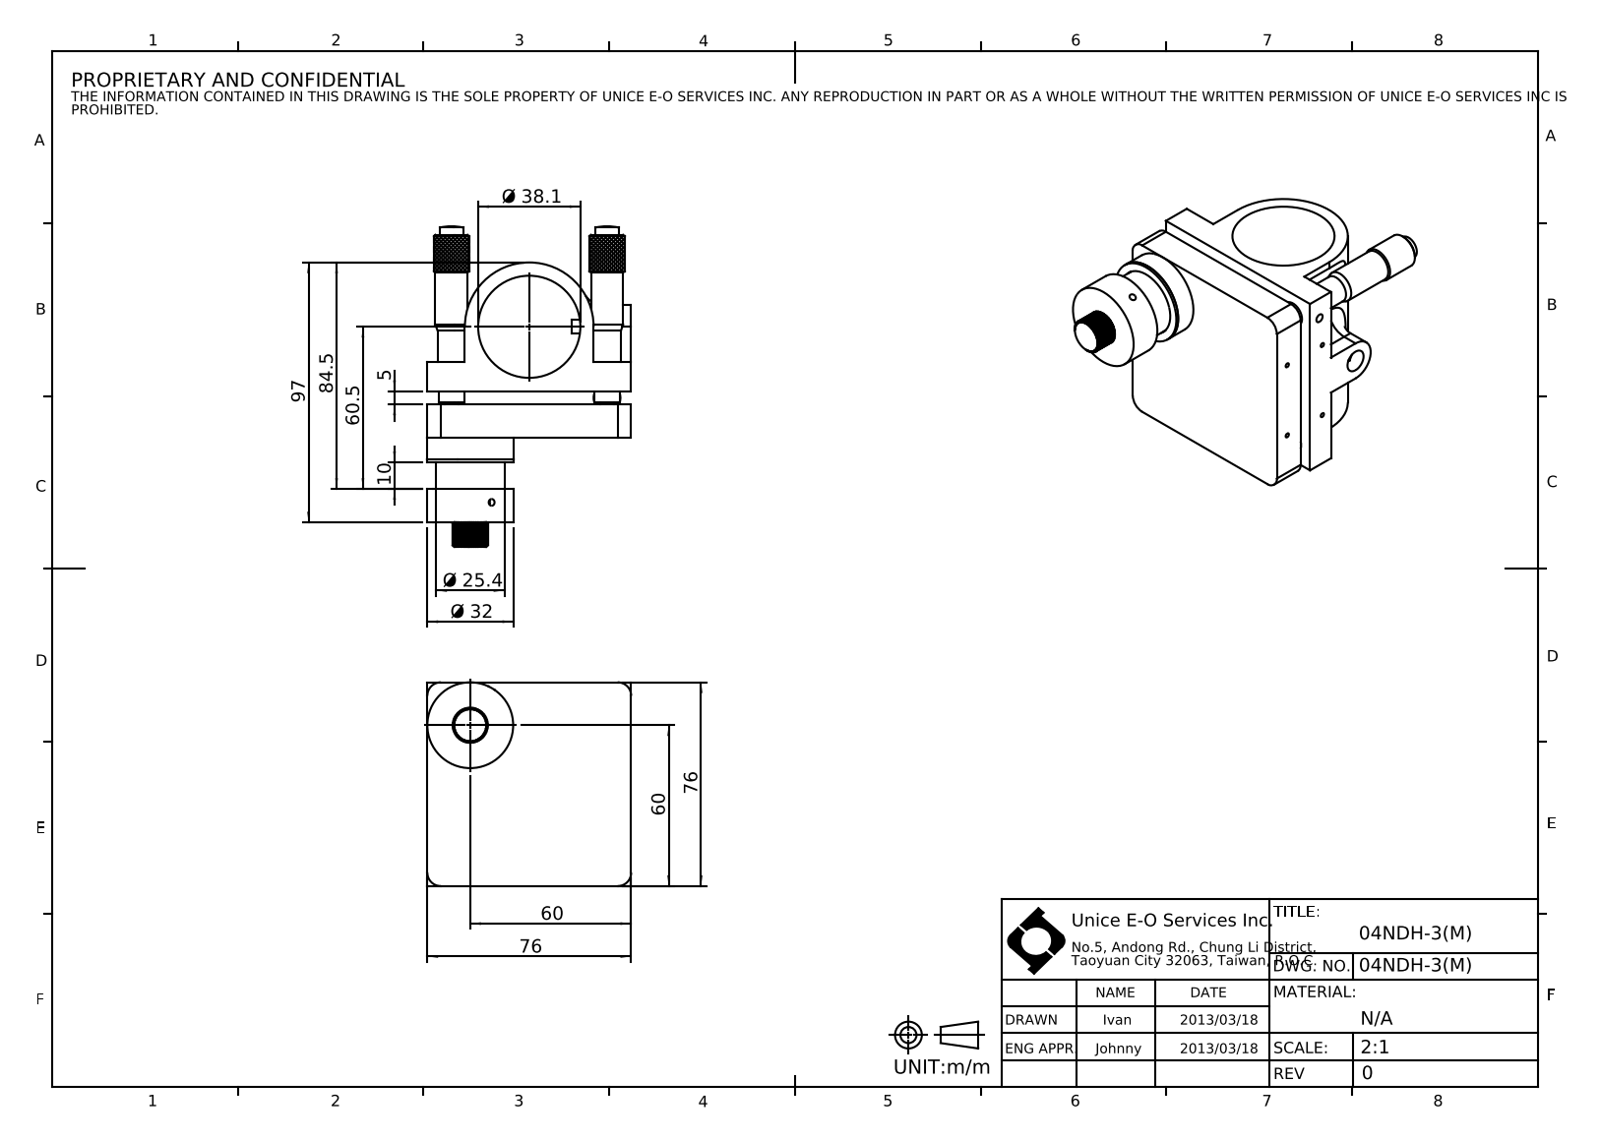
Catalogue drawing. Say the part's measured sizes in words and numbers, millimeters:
The part is named "04NDH-3(M)". Its 3-D file was written by "SolidWorks 2016 (CONFIG_CONTROL_DESIGN)". It is 11 solids with 371 faces: 171 planar, 166 cylindrical and 34 other. Overall it measures 119.5 by 76 by 76 millimeters. Its volume is 200 366 cubic millimeters and its surface area 63 656 square millimeters. Round holes: 4 of diameter 1.7, 3 of diameter 7, 2 of diameter 3.3, 2 of diameter 9.6, 1 of diameter 2.5, 1 of diameter 5, 1 of diameter 6.5, 1 of diameter 6.6, 1 of diameter 8, 1 of diameter 8.5, 1 of diameter 11, 1 of diameter 25.4. Round bosses or shafts: 3 of diameter 5, 2 of diameter 13, 2 of diameter 12, 2 of diameter 10.5, 2 of diameter 9.5, 2 of diameter 8.7, 1 of diameter 32, 1 of diameter 10. Partial cylindrical surfaces (rounded edges, fillets, slot ends): 5 of radius 8, 4 of radius 5, 1 of radius 6.5, 1 of radius 24. The main face-to-face distances are 12.5, 5, 17.5, 76, 11, 16, 28.5, 31.5, 14, 62. The hole center spacings are 32, 13, 13.09, 18.5, 21.4, 23.71, 34.67, 36.96.
